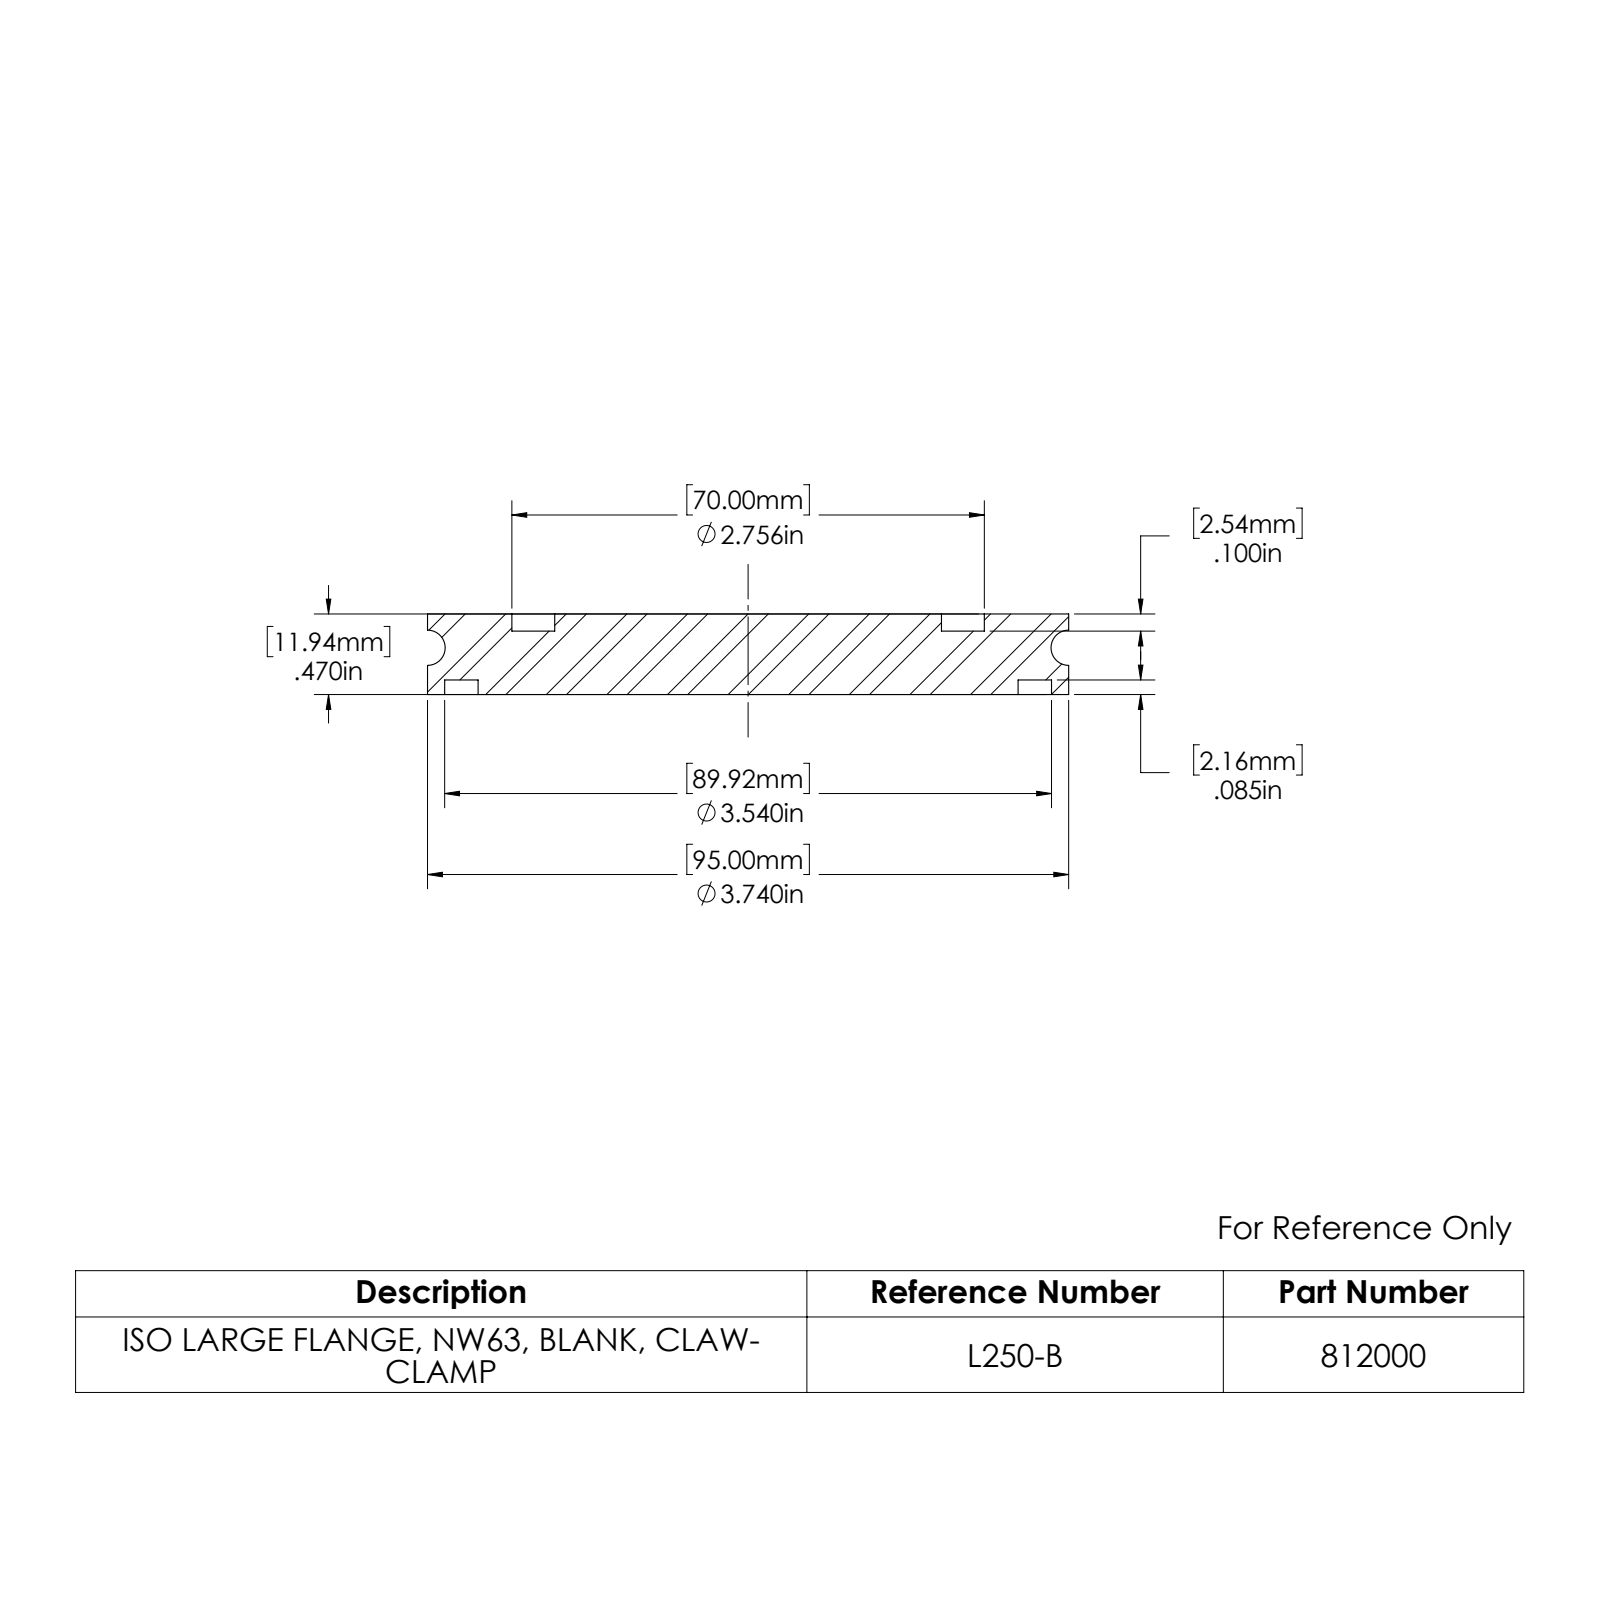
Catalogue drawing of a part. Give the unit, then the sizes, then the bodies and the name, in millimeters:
Units: millimetres
Overall size (bounding box): 95 × 95 × 11.9
Round holes (diameter × count): ⌀70 ×1, ⌀89.9 ×1
Round bosses / shafts (diameter × count): ⌀95 ×1, ⌀80 ×1, ⌀57.3 ×1
Main face-to-face distances: 11.9, 2.2, 9.8, 9.4, 7.2, 2.5
Volume: 75 400 mm³ · Surface area: 20 710 mm²
Bodies: 1 solid, 22 faces (6 planar, 12 cylindrical, 4 other)
Part name (STEP PRODUCT): 812000
STEP written by: SolidWorks 2022 (AUTOMOTIVE_DESIGN)
